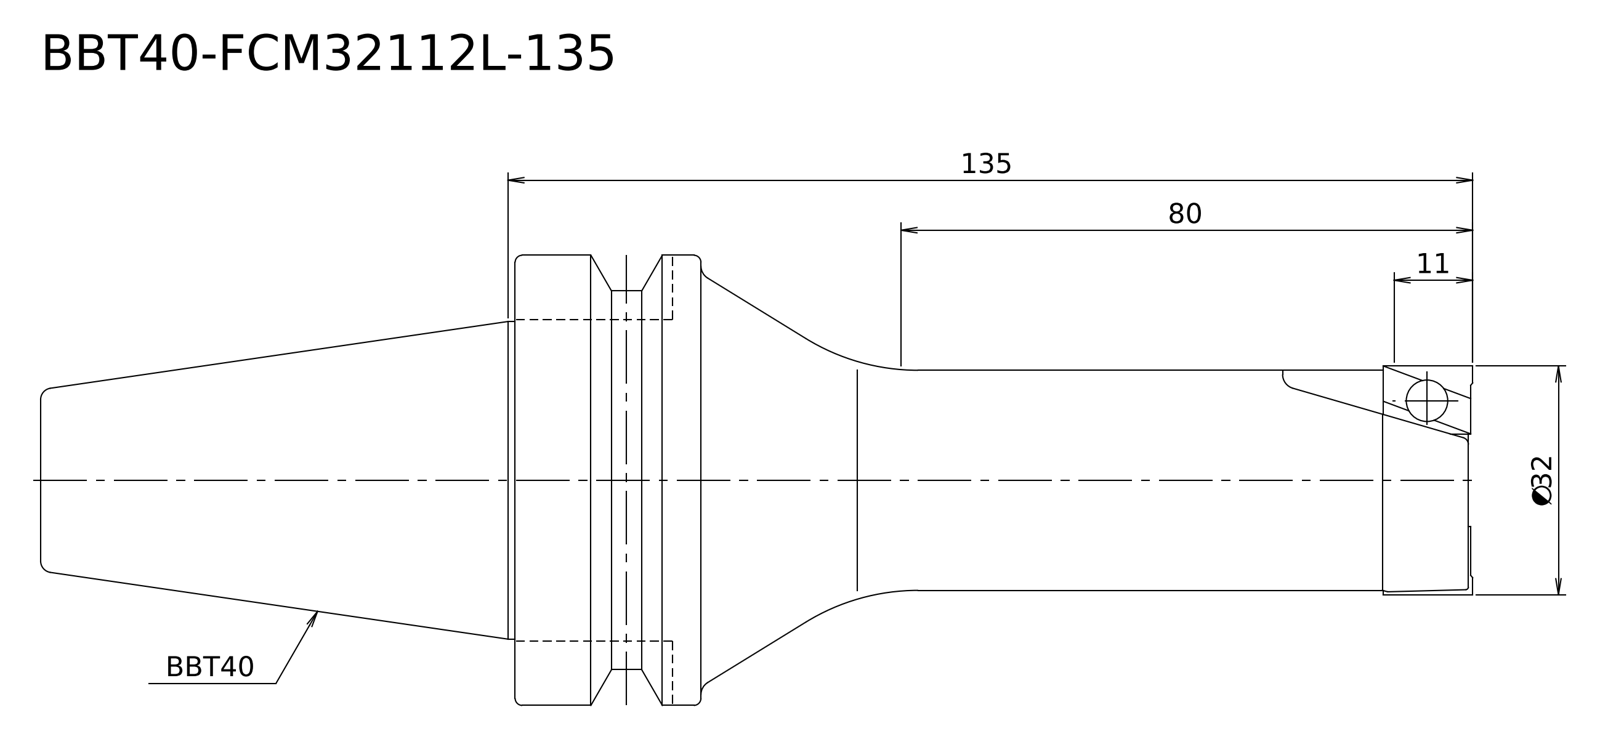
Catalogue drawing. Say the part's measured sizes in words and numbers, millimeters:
Its 3-D file was written by "Kubotek KeyCreator V8.5.1 (14335) (CONFIG_CONTROL_DESIGN)". It is 1 solid with 17 faces: 4 planar, 6 cylindrical and 7 other. Overall it measures 200.4 by 63 by 63 millimeters. Its volume is 241 933 cubic millimeters and its surface area 28 697 square millimeters. Round bosses or shafts: 1 of diameter 63, 1 of diameter 53, 1 of diameter 44.45, 1 of diameter 32, 1 of diameter 30.8. The main face-to-face distances are 134, 200.4, 66.4, 108, 26, 92.4.
